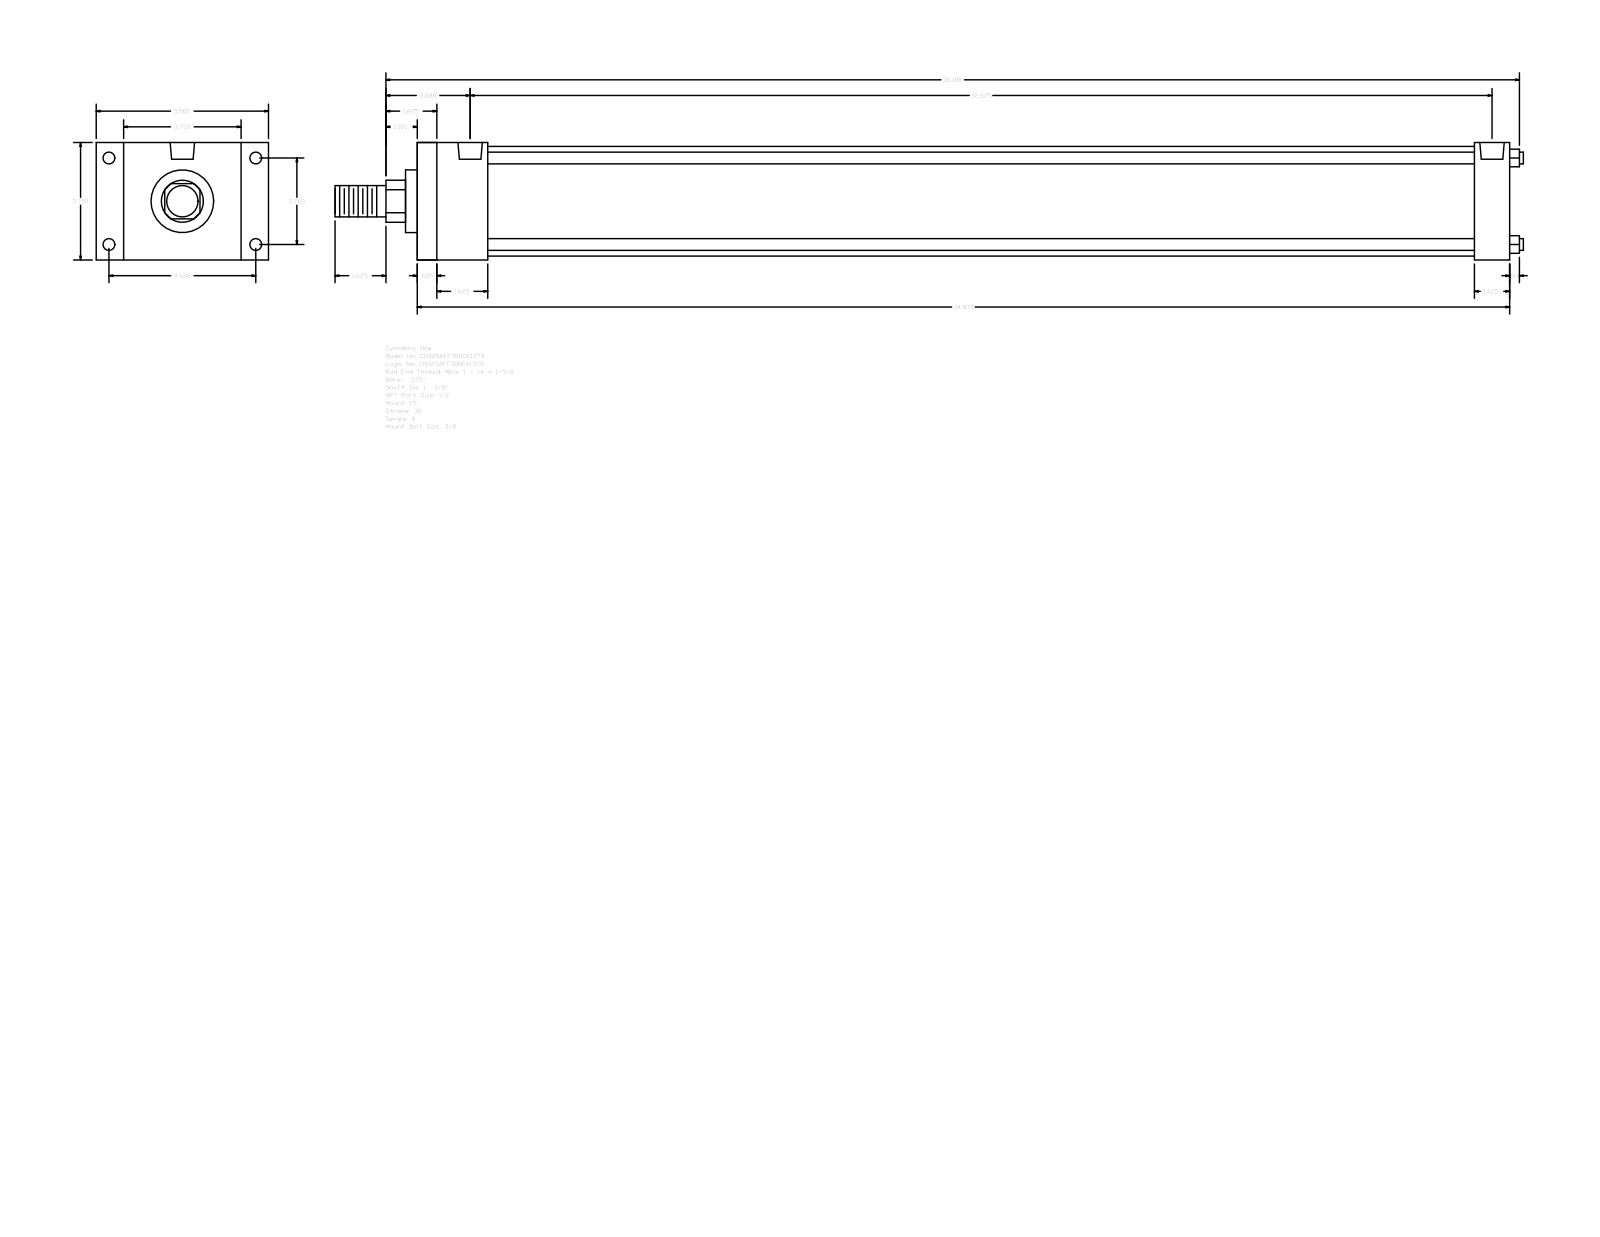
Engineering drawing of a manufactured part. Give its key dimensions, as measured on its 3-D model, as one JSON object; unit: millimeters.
{"part_name": "A_FF__0325_1.375", "step_written_by": "GSSL Pune (CONFIG_CONTROL_DESIGN)", "units": "millimeters", "bodies": {"solids": 0, "faces": 92, "planar": 64, "cylindrical": 28, "other": 0}, "overall_size": [963.61, 139.7, 95.25], "round_holes": [[8.73, 4], [9.53, 4], [19.77, 2]], "round_bosses_or_shafts": [[9.53, 4], [88.9, 1], [50.8, 1], [34.92, 1], [25.4, 1]], "partial_cylinders_radius": [[17.06, 1]], "face_to_face_distances": [95.24, 885.83, 15.87, 869.96, 57.15, 28.58, 22.23, 117.47, 857.25, 41.28], "hole_center_spacings": [3.18, 70.1, 119.06, 138.16, 822.32, 825.5, 828.68]}
